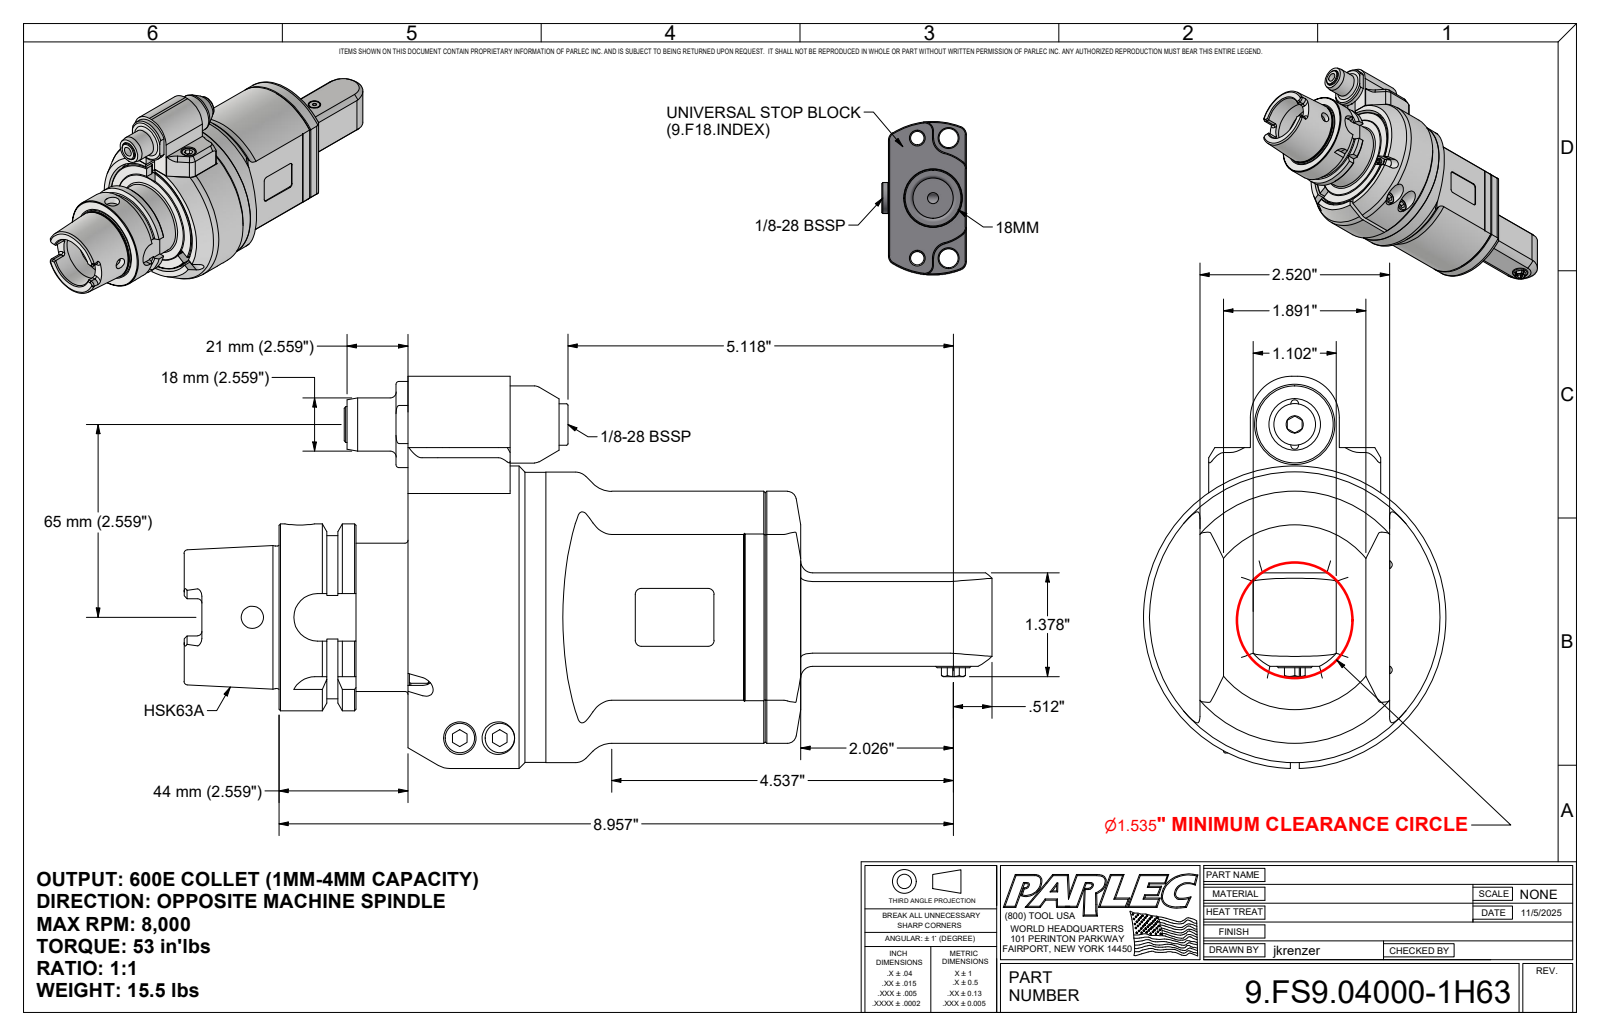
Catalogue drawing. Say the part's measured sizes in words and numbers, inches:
The part is named "9.FS9.04000-1H63; 9_FS9_04000; 9_GA1_566". Its 3-D file was written by "Autodesk Inventor 2025 (AUTOMOTIVE_DESIGN)". It is 5 solids with 541 faces: 272 planar, 139 cylindrical and 130 other. Overall it measures 10.728 by 5.206 by 4.016 inches. Its volume is 61.08 cubic inches and its surface area 226.4 square inches. Round holes: 2 of diameter 0.102, 2 of diameter 0.118, 2 of diameter 0.165, 2 of diameter 0.197, 2 of diameter 0.335, 2 of diameter 0.409, 2 of diameter 0.433, 2 of diameter 0.492, 1 of diameter 0.098, 1 of diameter 0.157, 1 of diameter 0.256, 1 of diameter 0.276. Round bosses or shafts: 4 of diameter 0.394, 4 of diameter 0.236, 3 of diameter 0.315, 2 of diameter 0.709, 2 of diameter 0.098, 1 of diameter 4.016, 1 of diameter 3.858, 1 of diameter 3.85. Partial cylindrical surfaces (rounded edges, fillets, slot ends): 12 of radius 0.079, 10 of radius 0.157, 6 of radius 0.059, 4 of radius 0.113, 4 of radius 0.315, 3 of radius 0.551, 2 of radius 0.02, 2 of radius 0.039. The main face-to-face distances are 0.709, 1.26, 0.02, 1.259, 1.024, 2.52, 0.276, 1.555, 1.102, 0.295. The hole center spacings are 0.276, 0.512, 0.551, 1.081, 1.72, 2.208, 2.283, 2.323.
